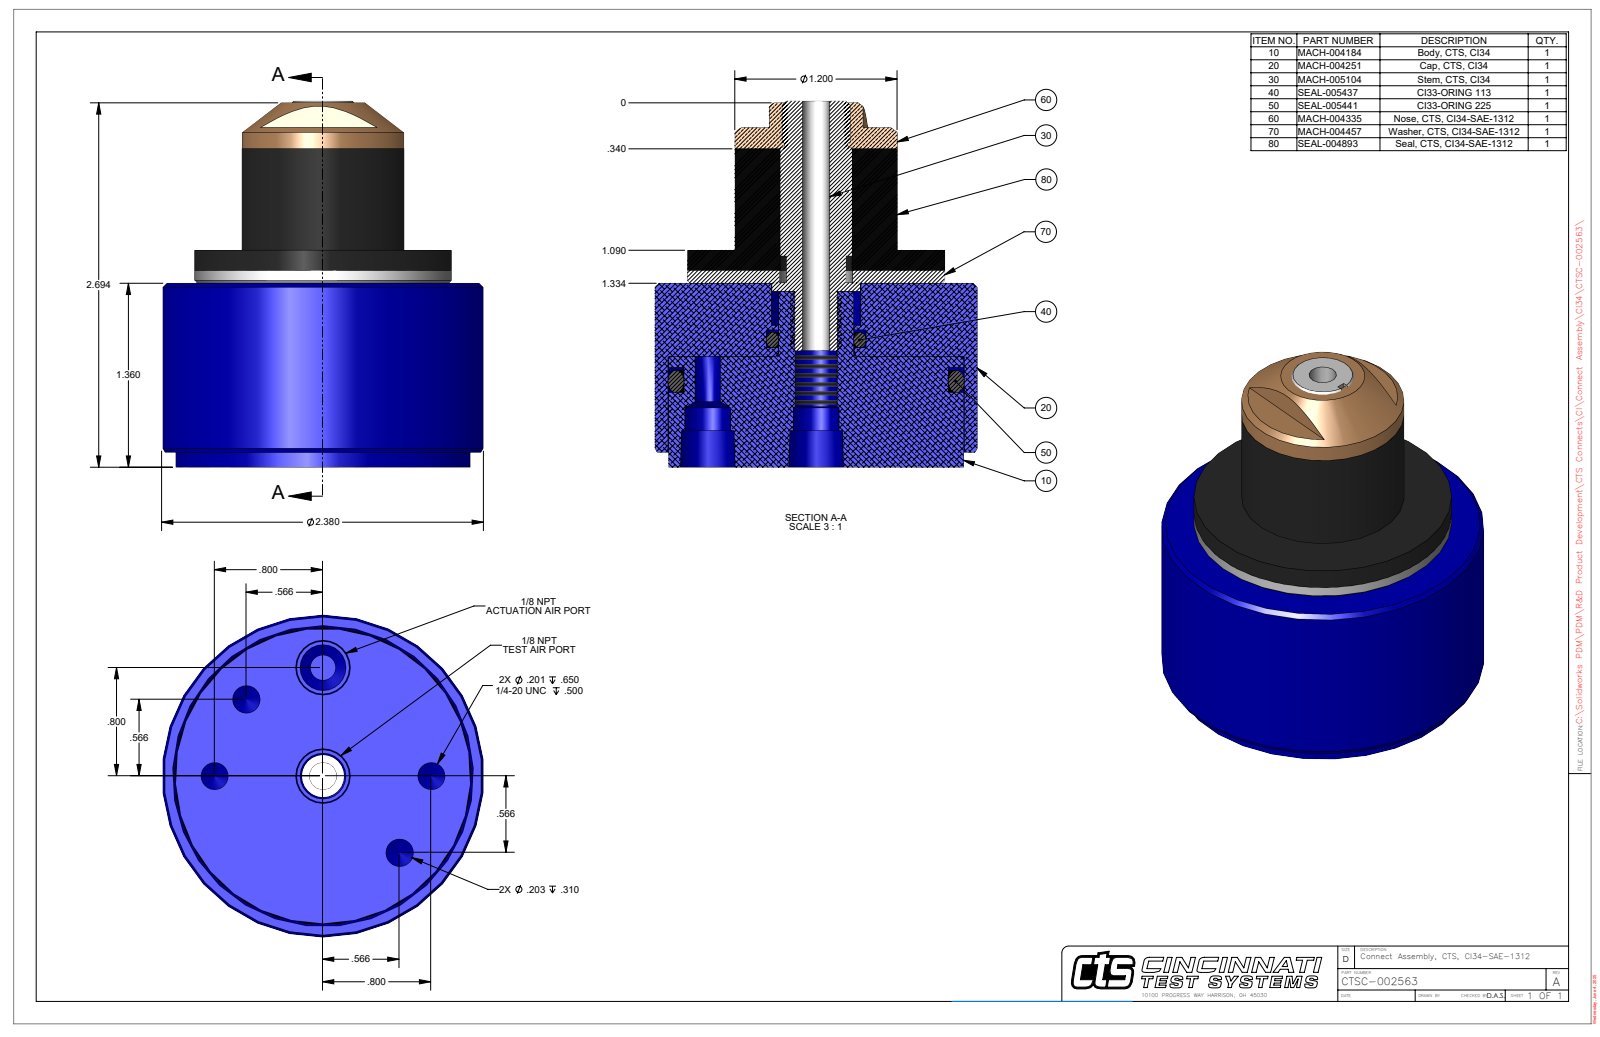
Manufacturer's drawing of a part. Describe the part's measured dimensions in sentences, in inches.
The part is named "CTSC-002563". Its 3-D file was written by "SolidWorks 2023 (AUTOMOTIVE_DESIGN)". It is 1 solid with 78 faces: 23 planar, 30 cylindrical and 25 other. Overall it measures 2.706 by 2.38 by 2.38 inches. Its volume is 7.539 cubic inches and its surface area 32.03 square inches. Round holes: 2 of diameter 0.201, 2 of diameter 0.203, 2 of diameter 0.339, 1 of diameter 0.203, 1 of diameter 0.661, 1 of diameter 2.188. Round bosses or shafts: 1 of diameter 2.38, 1 of diameter 2.178, 1 of diameter 1.9, 1 of diameter 1.2, 1 of diameter 0.65. Partial cylindrical surfaces (rounded edges, fillets, slot ends): 1 of radius 0.211. The main face-to-face distances are 1.604, 1.36, 0.244, 0.11, 1.25, 1.494, 2.51, 2.4, 1.15, 0.906. The hole center spacings are 0.8, 0.612, 1.478, 1.131, 1.6.
